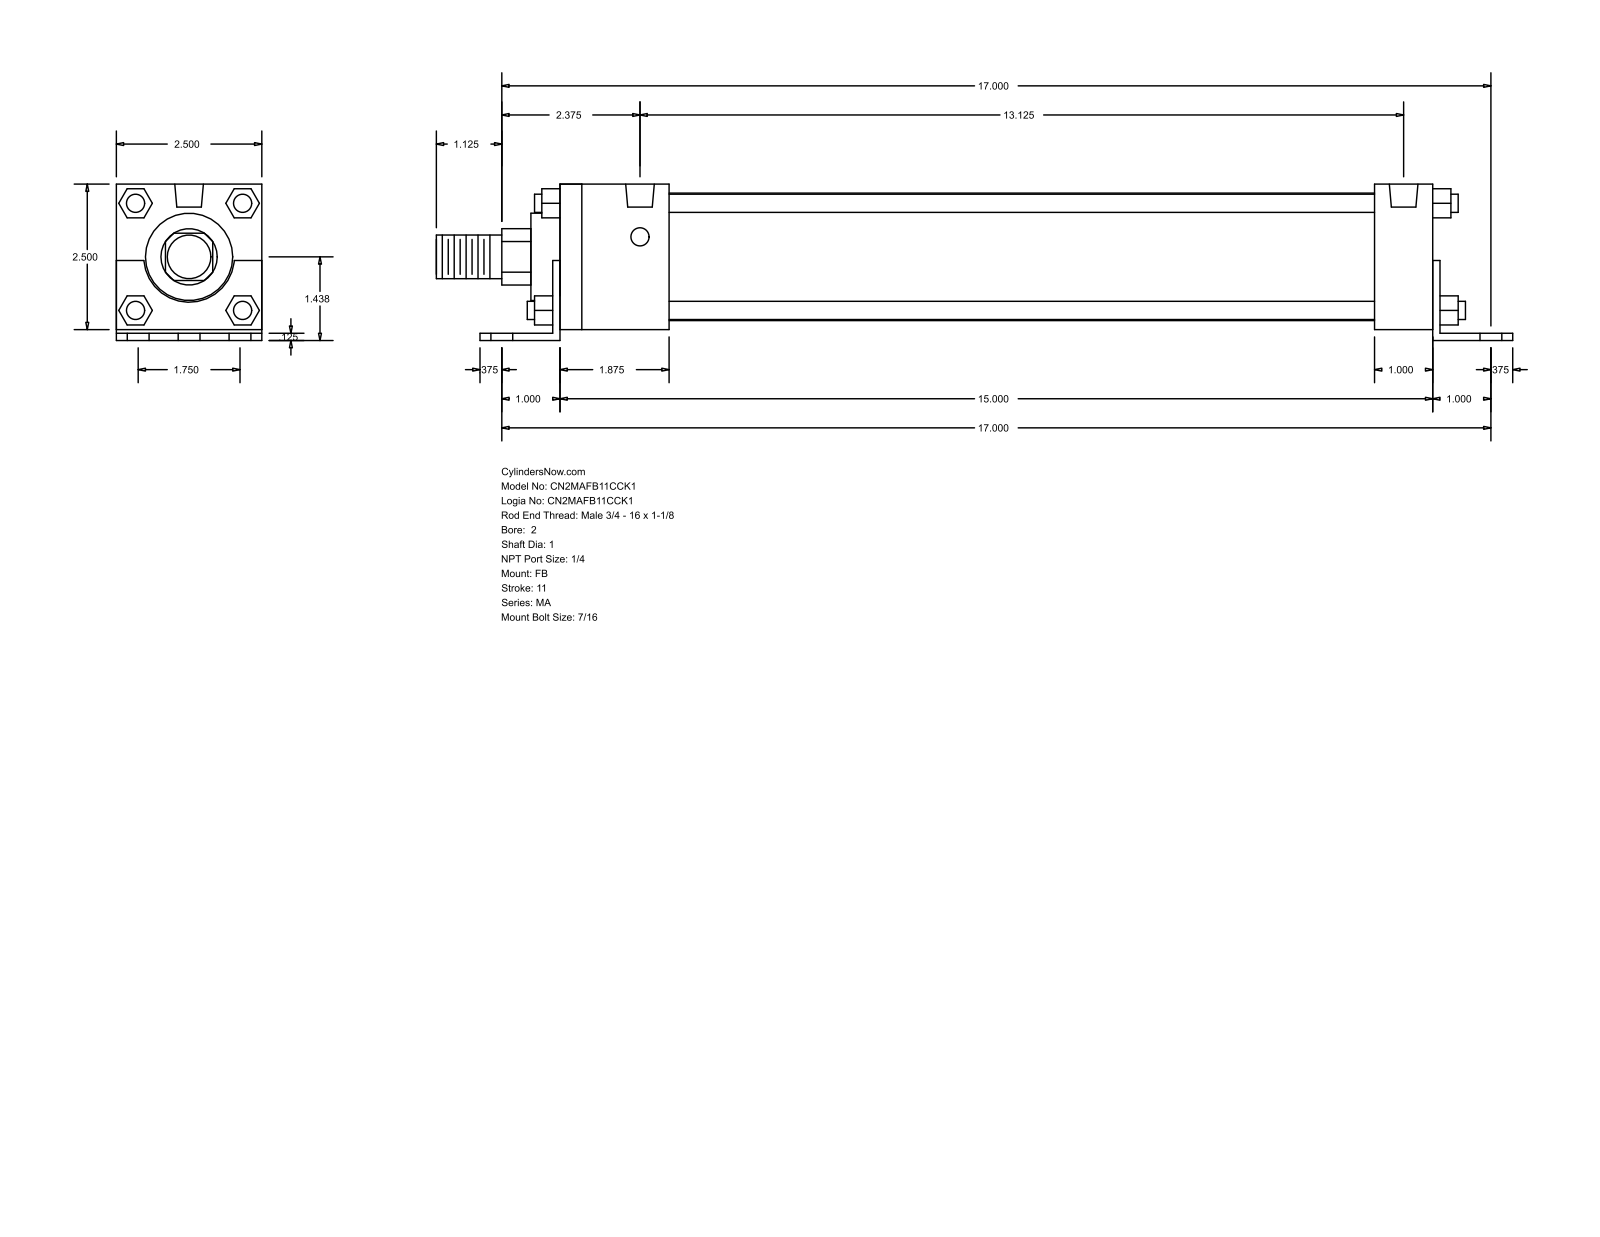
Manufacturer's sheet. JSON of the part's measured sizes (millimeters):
{"part_name": "MA_FB__0200_1", "step_written_by": "GSSL Pune (CONFIG_CONTROL_DESIGN)", "units": "millimeters", "bodies": {"solids": 0, "faces": 140, "planar": 105, "cylindrical": 35, "other": 0}, "overall_size": [469.9, 68.26, 63.5], "round_holes": [[11.11, 6], [7.94, 4], [12.49, 2]], "round_bosses_or_shafts": [[7.94, 4], [55.63, 1], [38.1, 1], [25.4, 1], [19.05, 1]], "partial_cylinders_radius": [[12.29, 1], [19.81, 1]], "face_to_face_distances": [63.5, 3.17, 4.76, 68.26, 1.59, 65.09, 384.17, 12.7, 381, 28.57], "hole_center_spacings": [22.23, 432.37, 431.8, 44.11, 44.46, 64.3, 333.37, 372.13]}
